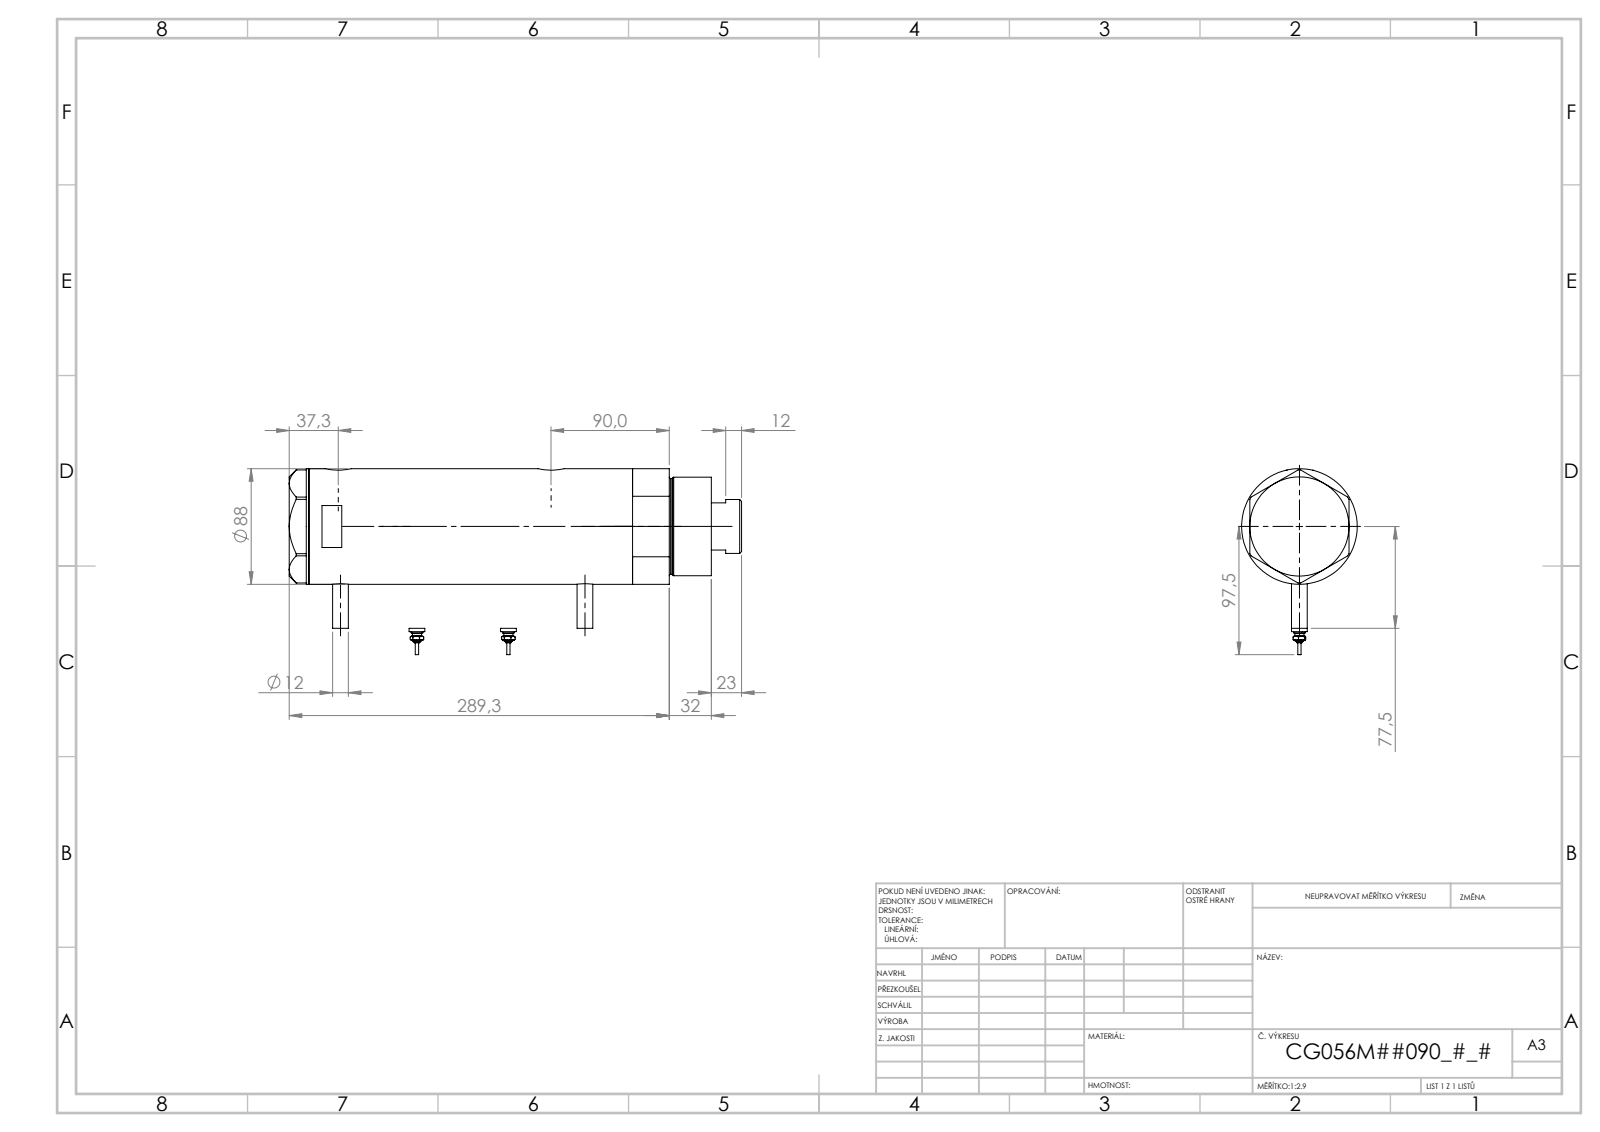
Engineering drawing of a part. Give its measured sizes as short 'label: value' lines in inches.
name: V270CG_FRONT; V270CG_VC; V270CG_MIDDLE; V270CG_BACK (+1 more)
written by: SolidWorks 2019 (CONFIG_CONTROL_DESIGN)
unit: in
bodies: 6 solids, 232 faces (81 planar, 77 cylindrical, 74 other)
size: 12.381 × 4.736 × 3.465
volume: 98.55 in³; area: 363.9 in²
holes: 2× ⌀0.197, 2× ⌀0.492, 2× ⌀0.518, 2× ⌀0.787, 1× ⌀0.571, 1× ⌀1.654, 1× ⌀1.713, 1× ⌀2.205, 1× ⌀2.362, 1× ⌀3.15
bosses: 2× ⌀0.472, 2× ⌀0.354, 2× ⌀0.276, 2× ⌀0.171, 2× ⌀0.094, 1× ⌀3.465, 1× ⌀2.953, 1× ⌀2.874
face distances: 6.472, 1.024, 5.449, 0.591, 1.614, 7.063, 10.885, 11.475, 9.861, 4.412
hole spacings: 0.067, 1.016, 5.524, 5.591, 6.539, 6.606
